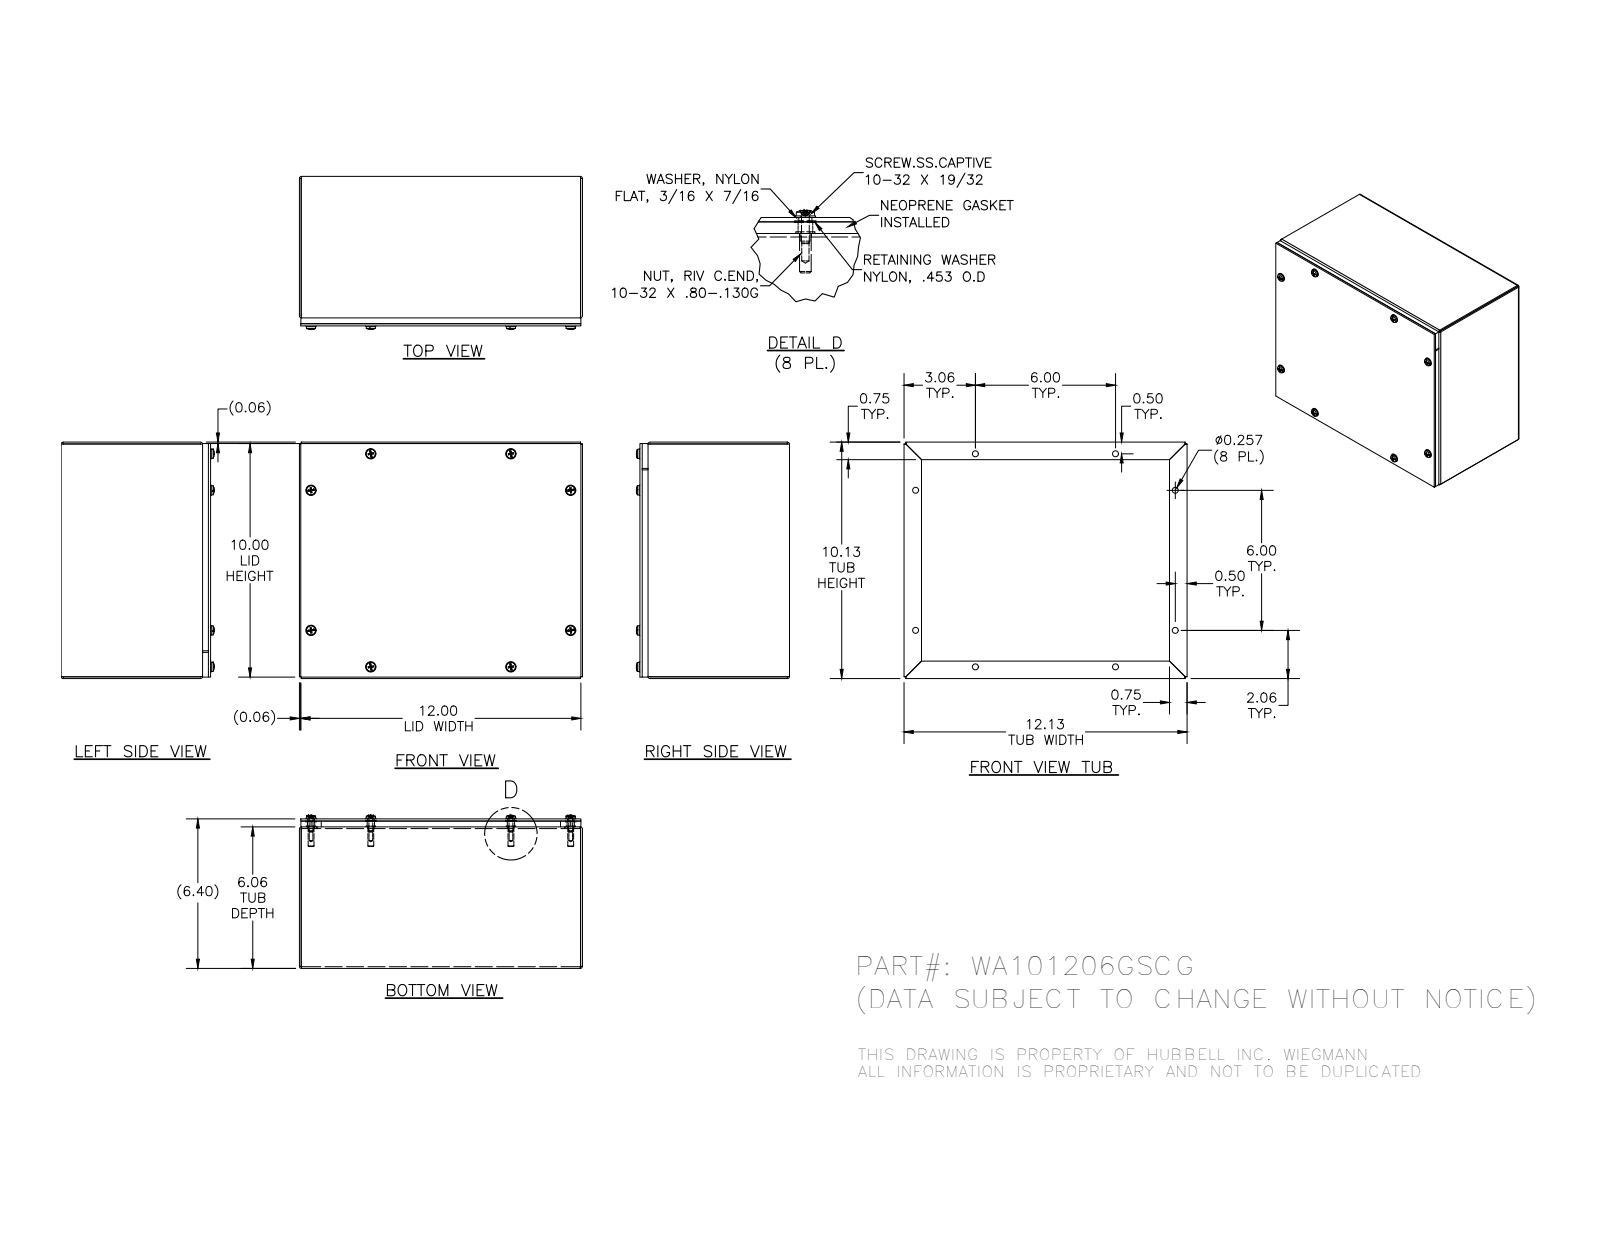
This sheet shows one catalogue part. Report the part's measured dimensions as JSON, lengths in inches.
{"part_name": "WA101206GSCG; WA101206GSCGBKP; 316281; WA1012GSCGLP (+4 more)", "step_written_by": "SolidWorks 2014 (AUTOMOTIVE_DESIGN)", "units": "inches", "bodies": {"solids": 36, "faces": 892, "planar": 420, "cylindrical": 240, "other": 232}, "overall_size": [12.125, 10.125, 6.558], "volume_in3": 50.82, "surface_area_in2": 1187, "round_holes": [[0.156, 8], [0.188, 8], [0.196, 8], [0.257, 8], [0.278, 8], [0.281, 8], [0.313, 8]], "round_bosses_or_shafts": [[0.453, 8], [0.437, 8], [0.406, 8], [0.248, 8], [0.167, 8]], "partial_cylinders_radius": [[0.016, 8], [0.089, 8], [0.09, 8]], "face_to_face_distances": [0.074, 10.051, 0.094, 6.33, 6.236, 6.404, 6.31, 5.986, 10.125, 9.977], "hole_center_spacings": [6, 7.985, 7.985, 11.424, 3.001, 8.703, 11.424, 3.001]}
